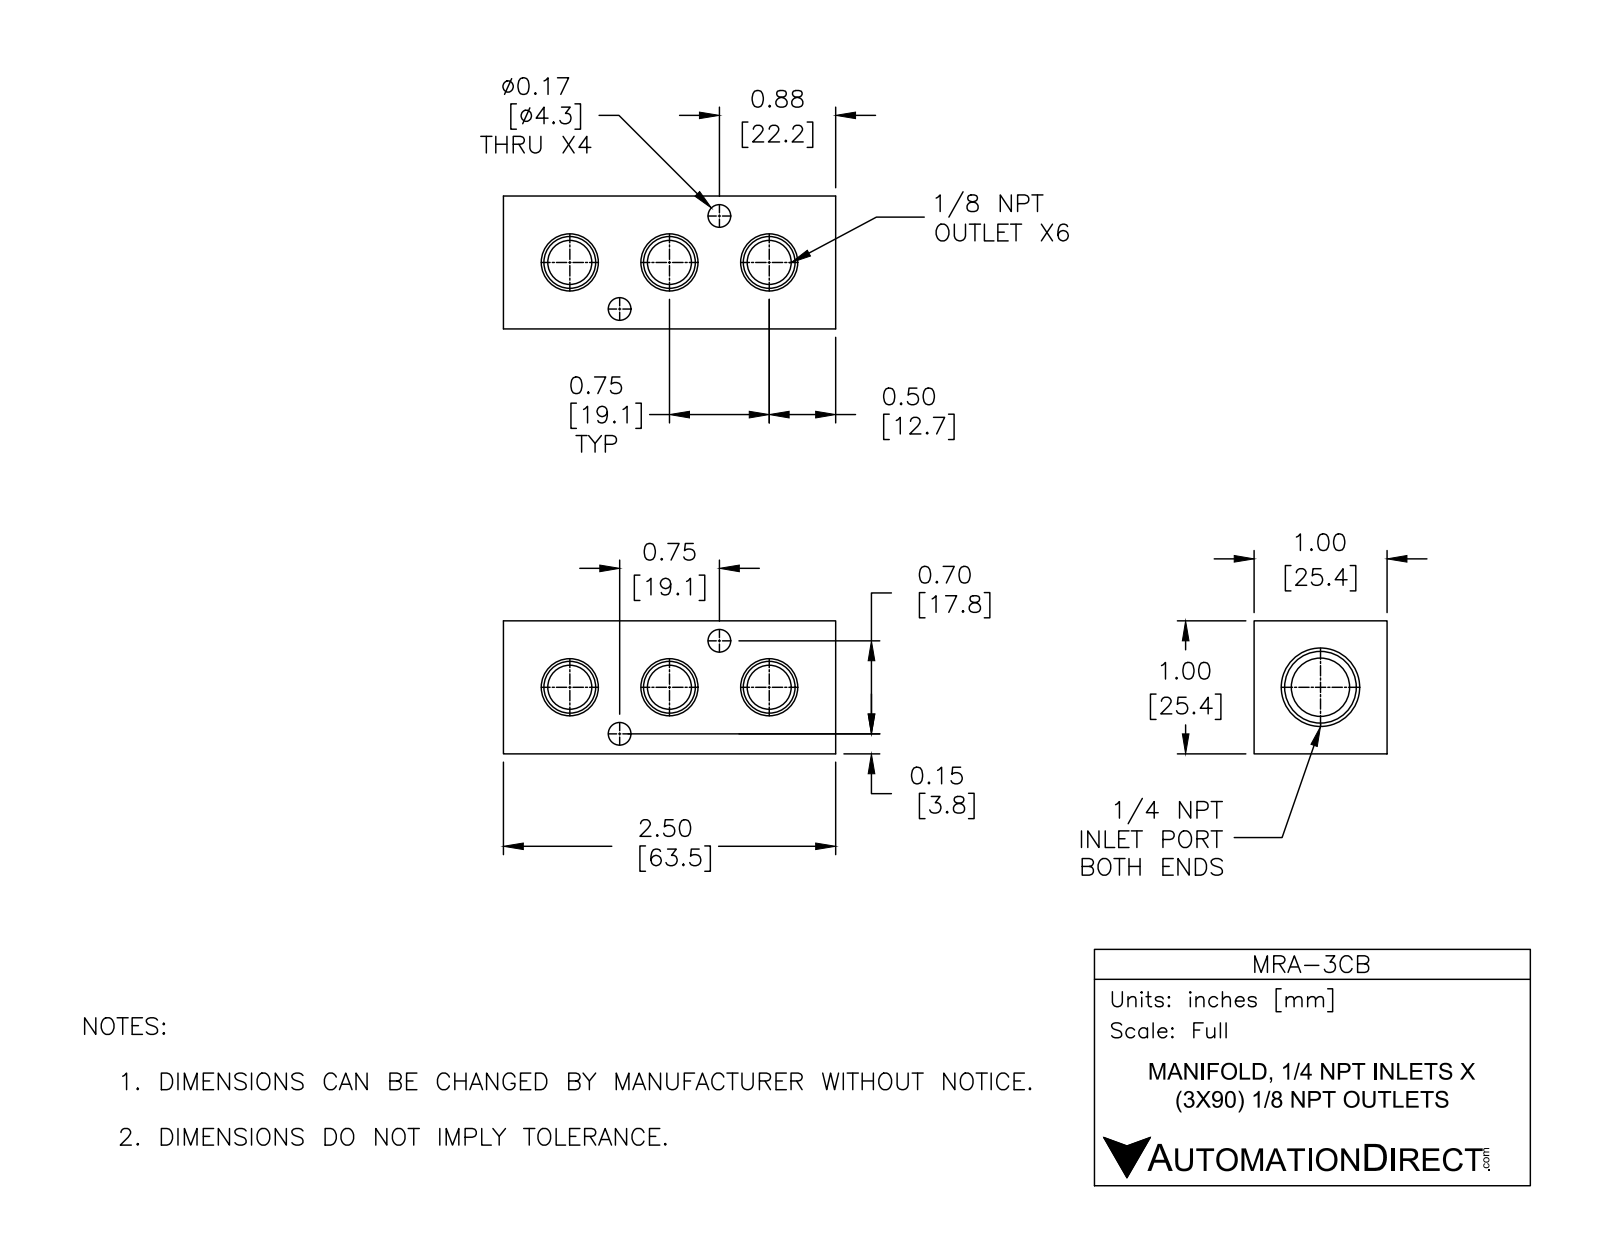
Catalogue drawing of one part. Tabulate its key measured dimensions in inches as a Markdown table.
| quantity | value |
| --- | --- |
| part name | MRA-3CB-90 |
| STEP written by | SolidWorks 2015 (CONFIG_CONTROL_DESIGN) |
| units | inches |
| bodies | 1 solid, 78 faces (16 planar, 30 cylindrical, 32 other) |
| overall size | 2.5 × 1 × 1 |
| volume | 1.77 in³ |
| surface area | 17.96 in² |
| round holes (diameter × count) | 0.17 × 4, 0.332 × 2, 0.438 × 1 |
| partial cylindrical surfaces (radius × count) | 0.166 × 4 |
| main face-to-face distances | 1, 2.5, 0.27, 0.73, 0.39, 2.11, 1.72 |
| hole center spacings | 0.513, 1.026 |
